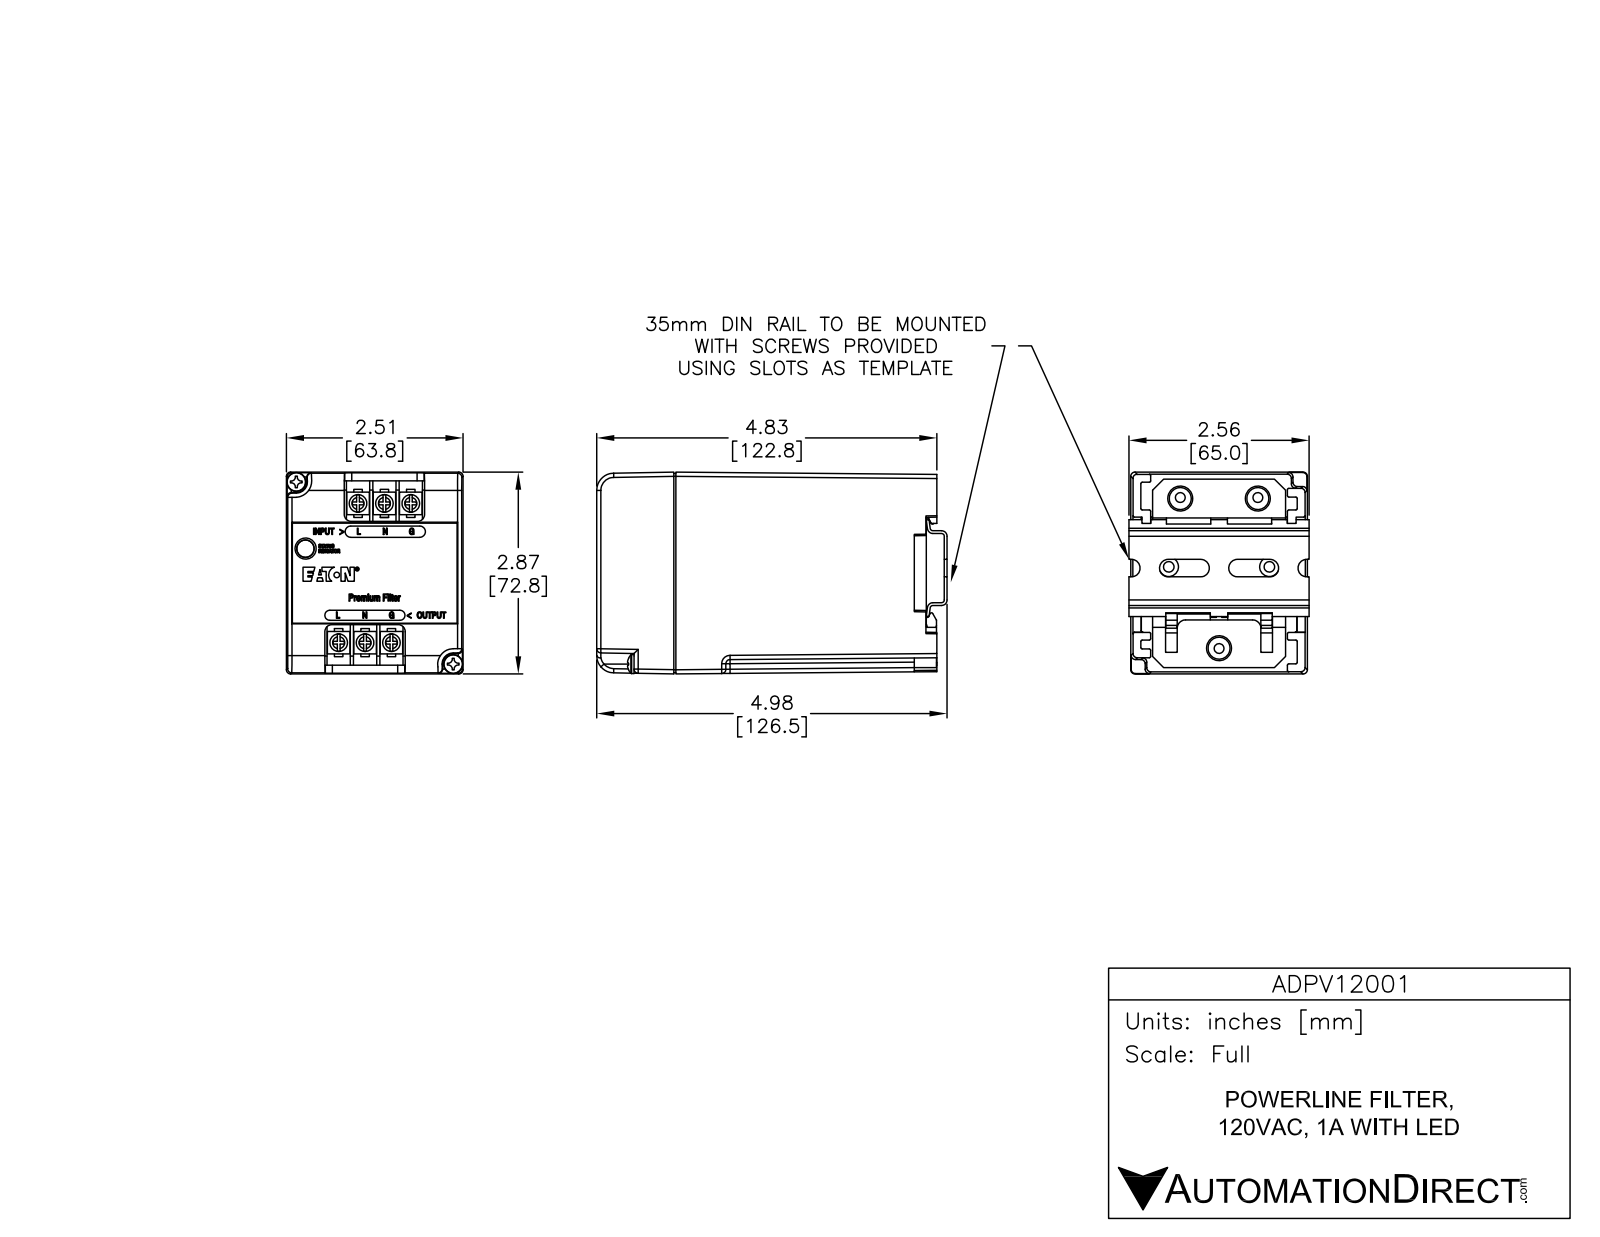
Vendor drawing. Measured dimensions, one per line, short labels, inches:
name: AD-PV12001
written by: SolidWorks 2013 (AUTOMOTIVE_DESIGN)
unit: in
bodies: 27 solids, 654 faces (497 planar, 97 cylindrical, 60 other)
size: 4.934 × 2.867 × 2.509
volume: 32.2 in³; area: 124.4 in²
holes: 3× ⌀0.313, 2× ⌀0.153, 1× ⌀0.249
bosses: 6× ⌀0.25, 6× ⌀0.07, 5× ⌀0.236, 2× ⌀0.26
rounds: 17× R0.025, 6× R0.124, 4× R0.039, 4× R0.079, 4× R0.25, 2× R0.15
face distances: 3.39, 0.15, 4.51, 1.12, 0.605, 4.25, 4.4, 3.905, 0.515, 0.195
hole spacings: 2.214, 0.604, 0.843, 0.956, 1.102, 1.133, 1.678, 1.698
